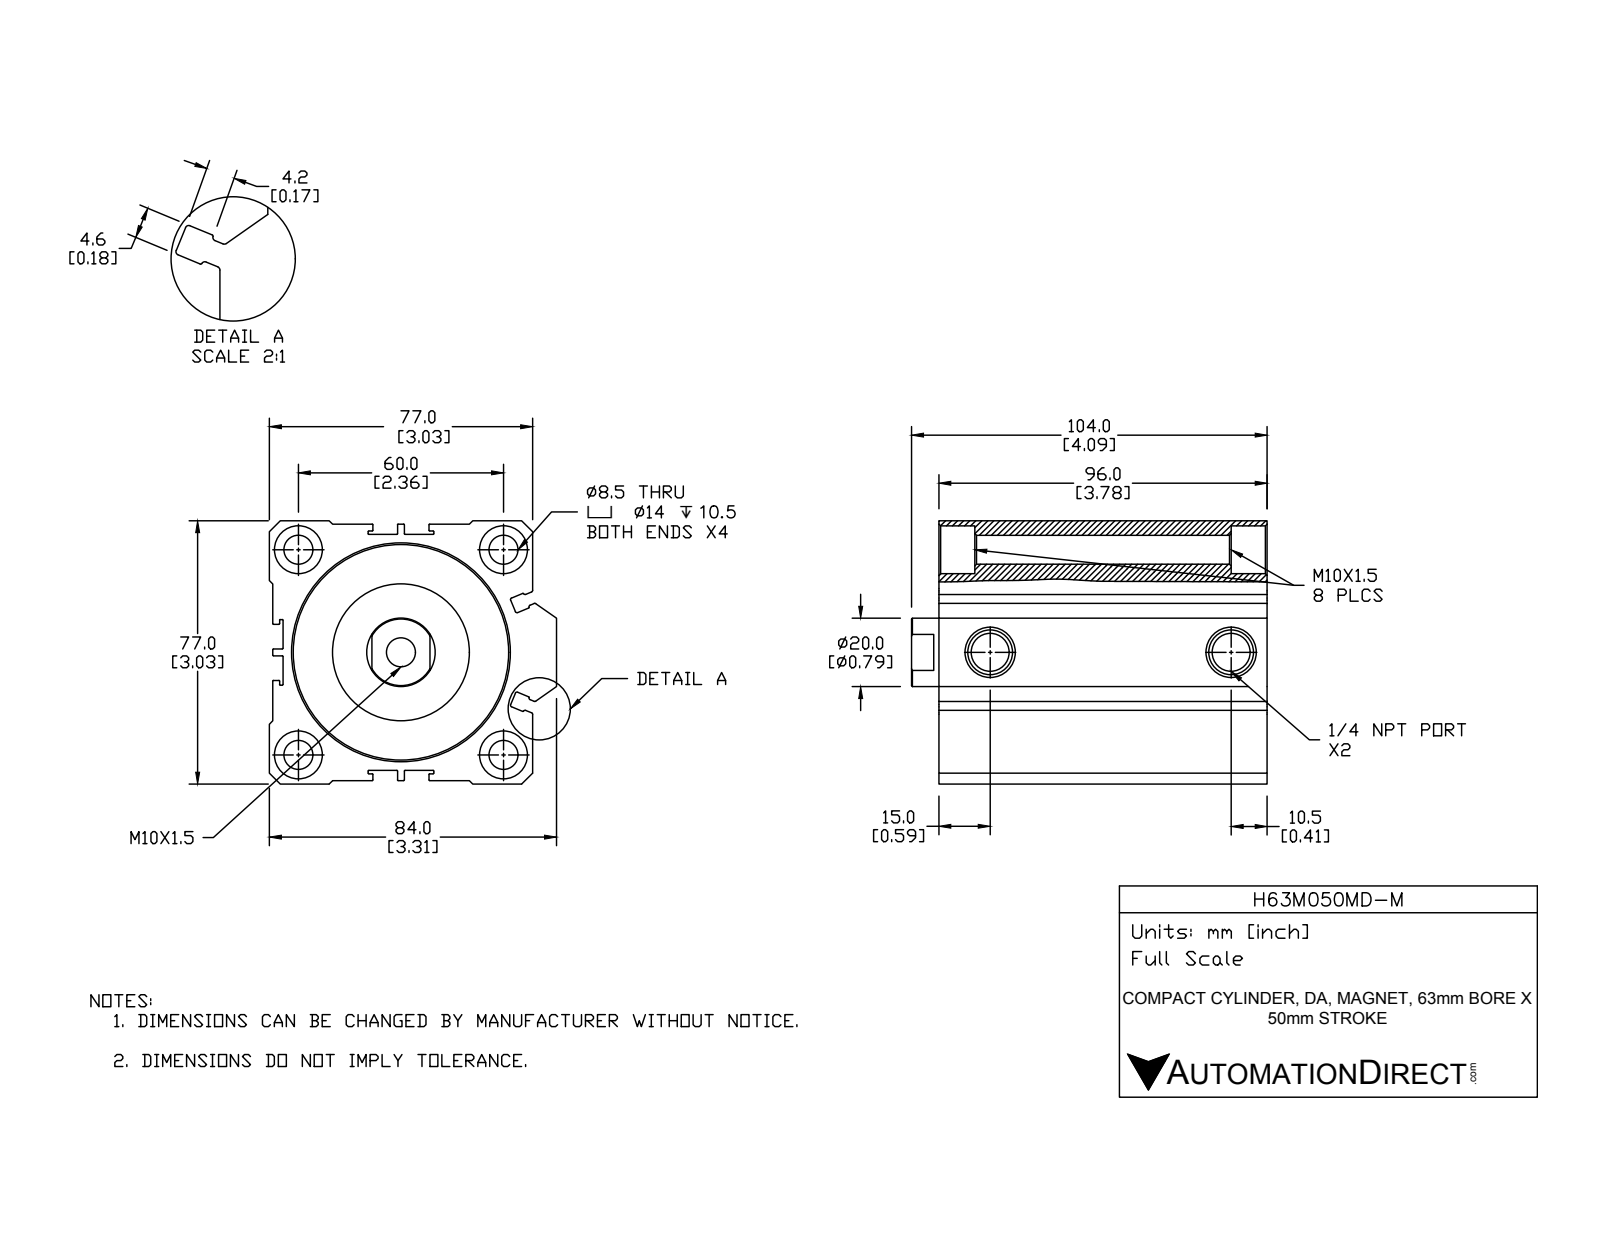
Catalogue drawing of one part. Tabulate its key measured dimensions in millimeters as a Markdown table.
| quantity | value |
| --- | --- |
| part name | H63M050MD-M-PISTON; H63M050MD-M-BODY; H63M050MD-M |
| STEP written by | SolidWorks 2015 (CONFIG_CONTROL_DESIGN) |
| units | millimeters |
| bodies | 2 solids, 255 faces (99 planar, 103 cylindrical, 53 other) |
| overall size | 104 × 84 × 77 |
| volume | 363 336 mm³ |
| surface area | 99 881 mm² |
| round holes (diameter × count) | 8.5 × 5, 14 × 4, 11.13 × 2, 20 × 1, 45.51 × 1, 63 × 1 |
| round bosses / shafts (diameter × count) | 40 × 1, 39 × 1 |
| partial cylindrical surfaces (radius × count) | 0.2 × 40, 0.5 × 12 |
| main face-to-face distances | 1, 76, 3, 77, 4, 73, 2, 72, 23, 73.5 |
| hole center spacings | 42.43, 60, 84.85, 70.5 |
